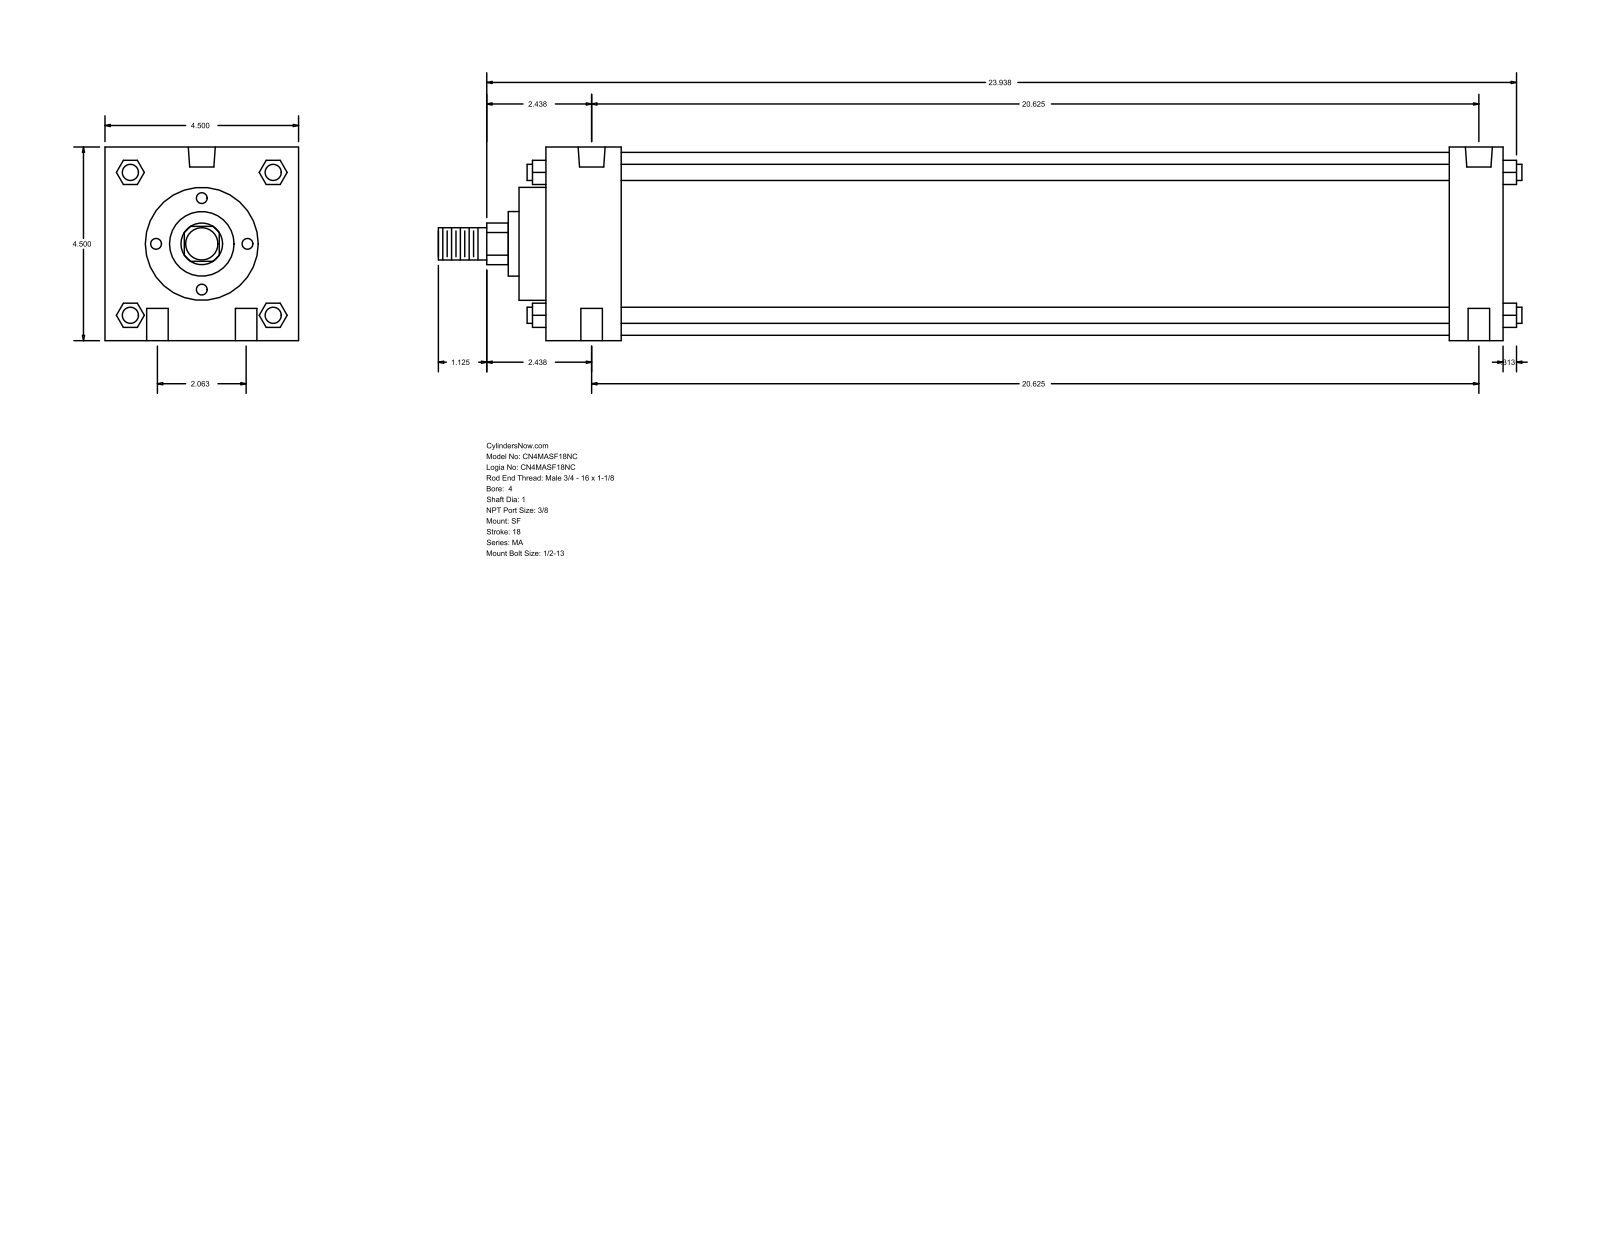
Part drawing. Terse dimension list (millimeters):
name: MA_SF__0400_1
written by: GSSL Pune (CONFIG_CONTROL_DESIGN)
unit: mm
bodies: 0 solids, 126 faces (95 planar, 31 cylindrical, 0 other)
size: 639.76 × 114.3 × 114.3
holes: 4× ⌀12.7, 2× ⌀11.11, 2× ⌀15.93
bosses: 4× ⌀9.53, 1× ⌀107.95, 1× ⌀66.67, 1× ⌀38.1, 1× ⌀25.4, 1× ⌀19.05
rounds: 1× R12.29
face distances: 114.3, 565.16, 533.41, 31.75, 44.46, 488.95, 520.7, 15.87, 60.33, 549.28
hole spacings: 26.19, 524.53, 523.88, 52.38, 526.49, 514.35
